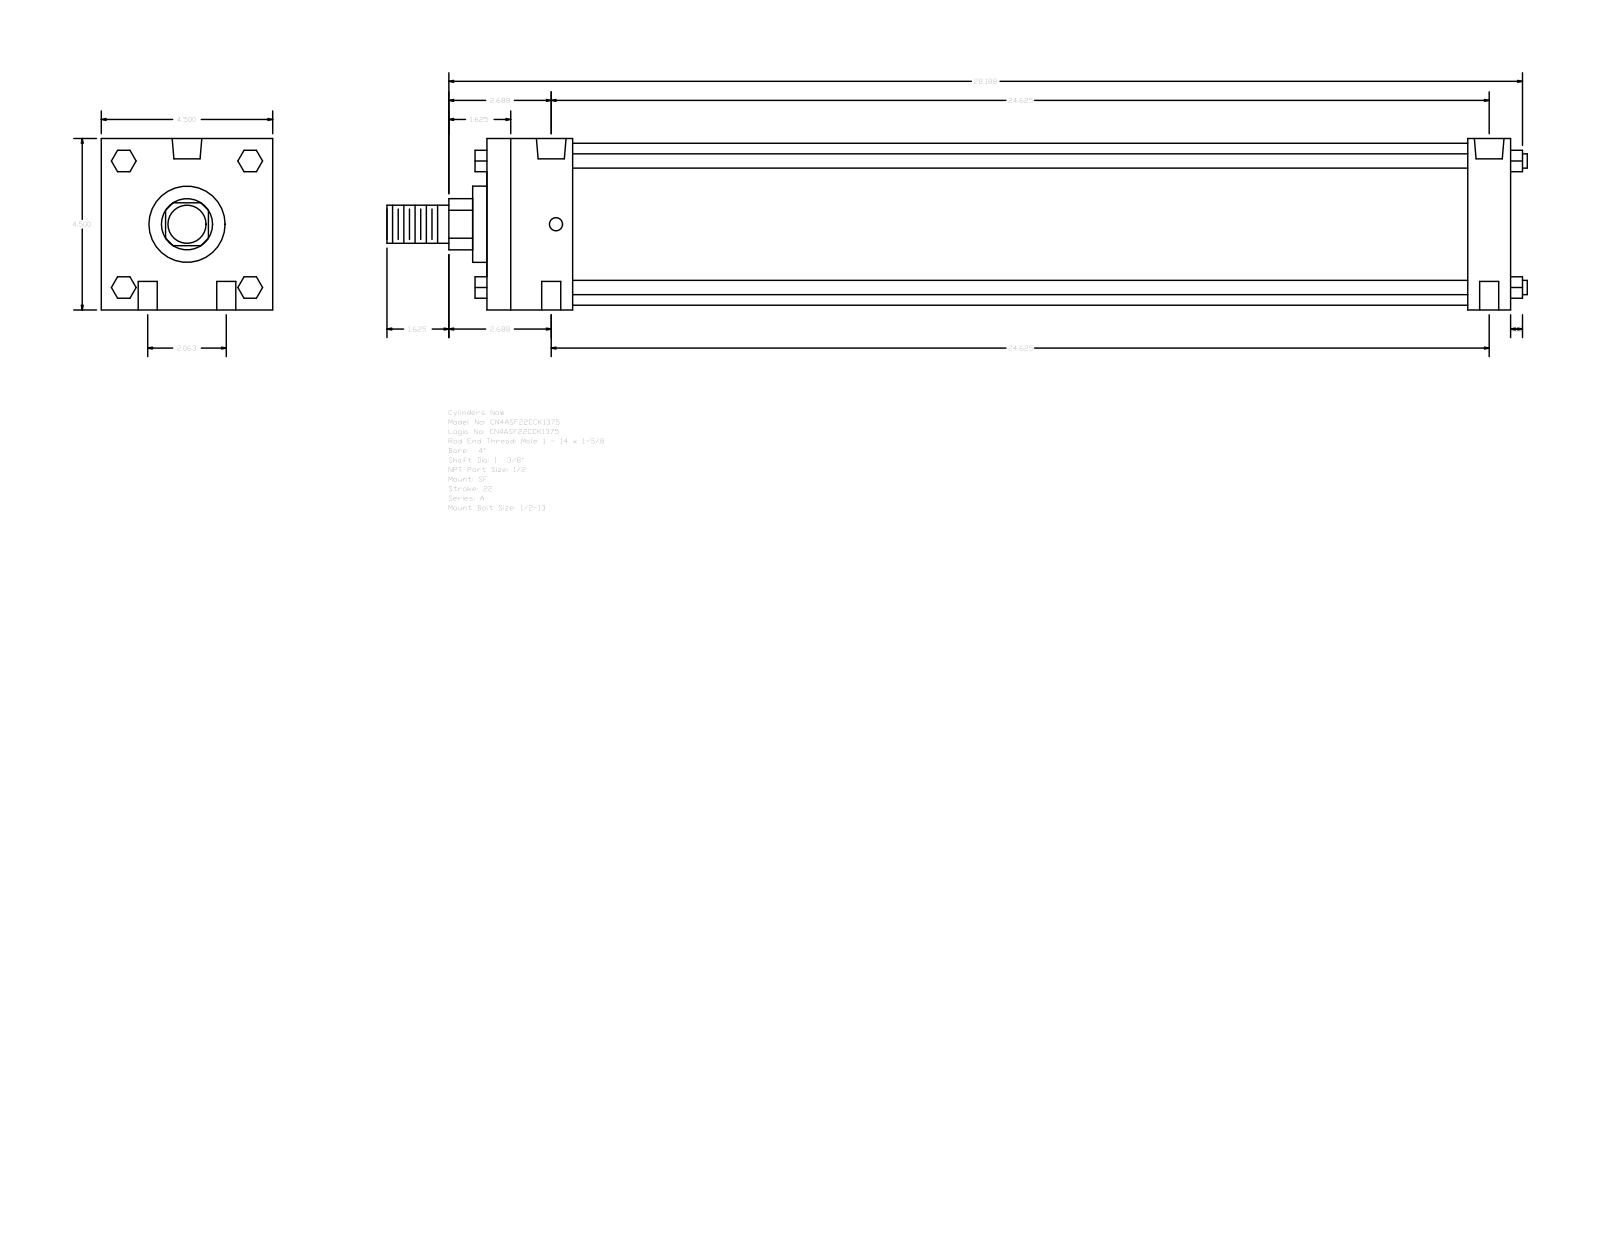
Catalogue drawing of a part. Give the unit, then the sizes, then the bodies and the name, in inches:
Units: inches
Overall size (bounding box): 29.937 × 4.5 × 4.5
Round holes (diameter × count): ⌀0.5 ×4, ⌀0.344 ×2, ⌀0.778 ×2
Round bosses / shafts (diameter × count): ⌀0.375 ×4, ⌀4.25 ×1, ⌀2 ×1, ⌀1.375 ×1, ⌀1 ×1
Partial cylindrical surfaces — rounded edges, fillets, slot ends (radius × count): R0.672 ×1
Main face-to-face distances: 4.5, 26.875, 2.25, 25.75, 1.125, 23.5, 24.625, 2.625, 0.563, 0.375
Hole centre spacings: 1.031, 24.647, 24.625, 2.062, 24.711, 24.375
Bodies: 0 solids, 124 faces (94 planar, 30 cylindrical, 0 other)
Part name (STEP PRODUCT): A_SF__0400_1.375
STEP written by: GSSL Pune (CONFIG_CONTROL_DESIGN)
